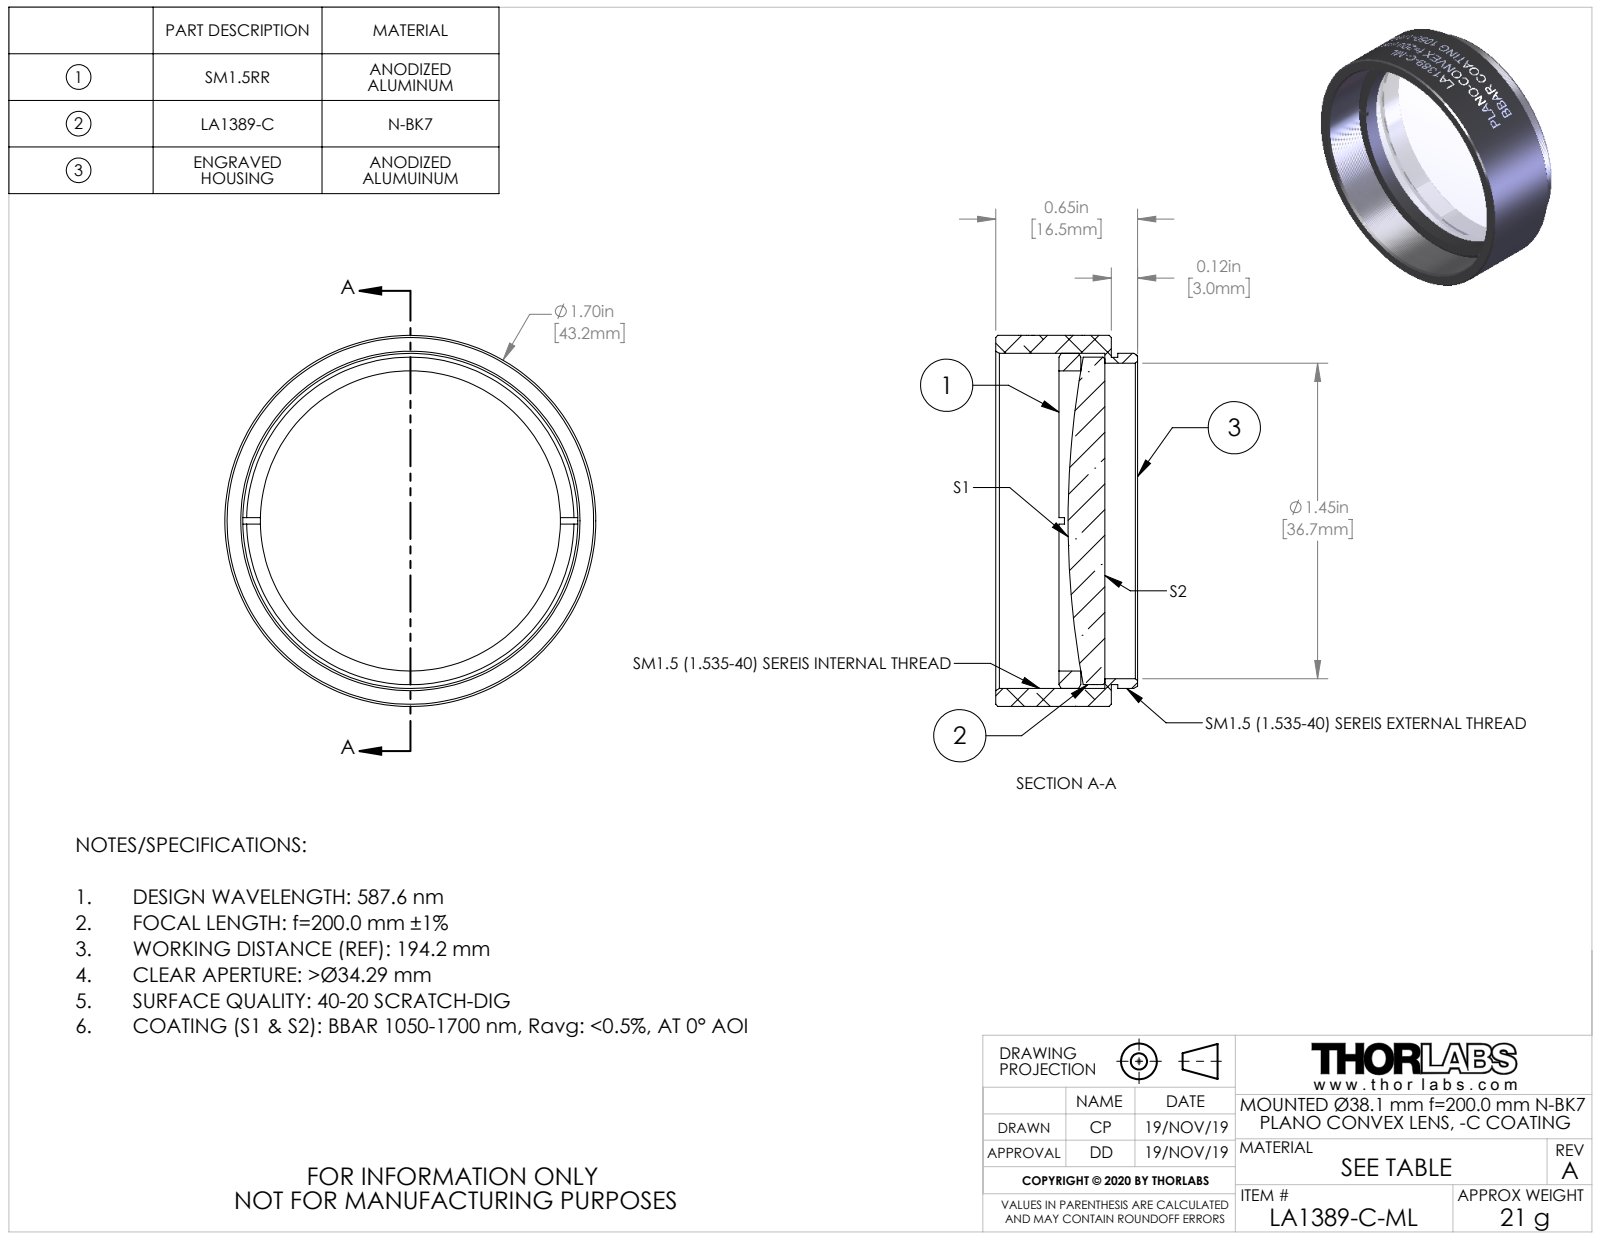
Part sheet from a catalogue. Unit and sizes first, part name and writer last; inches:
Units: inches
Overall size (bounding box): 1.7 × 1.7 × 0.65
Round holes (diameter × count): ⌀1.375 ×1, ⌀1.445 ×1
Round bosses / shafts (diameter × count): ⌀1.7 ×1, ⌀1.535 ×1, ⌀1.5 ×1, ⌀1.499 ×1
Main face-to-face distances: 0.03, 0.53, 0.5, 0.14, 0.109, 0.391, 0.24, 0.209, 0.1, 0.291
Volume: 0.521 in³ · Surface area: 13.34 in²
Bodies: 3 solids, 160 faces (15 planar, 126 cylindrical, 19 other)
Part name (STEP PRODUCT): TTN200749-E0W
STEP written by: SolidWorks 2018 (CONFIG_CONTROL_DESIGN)
